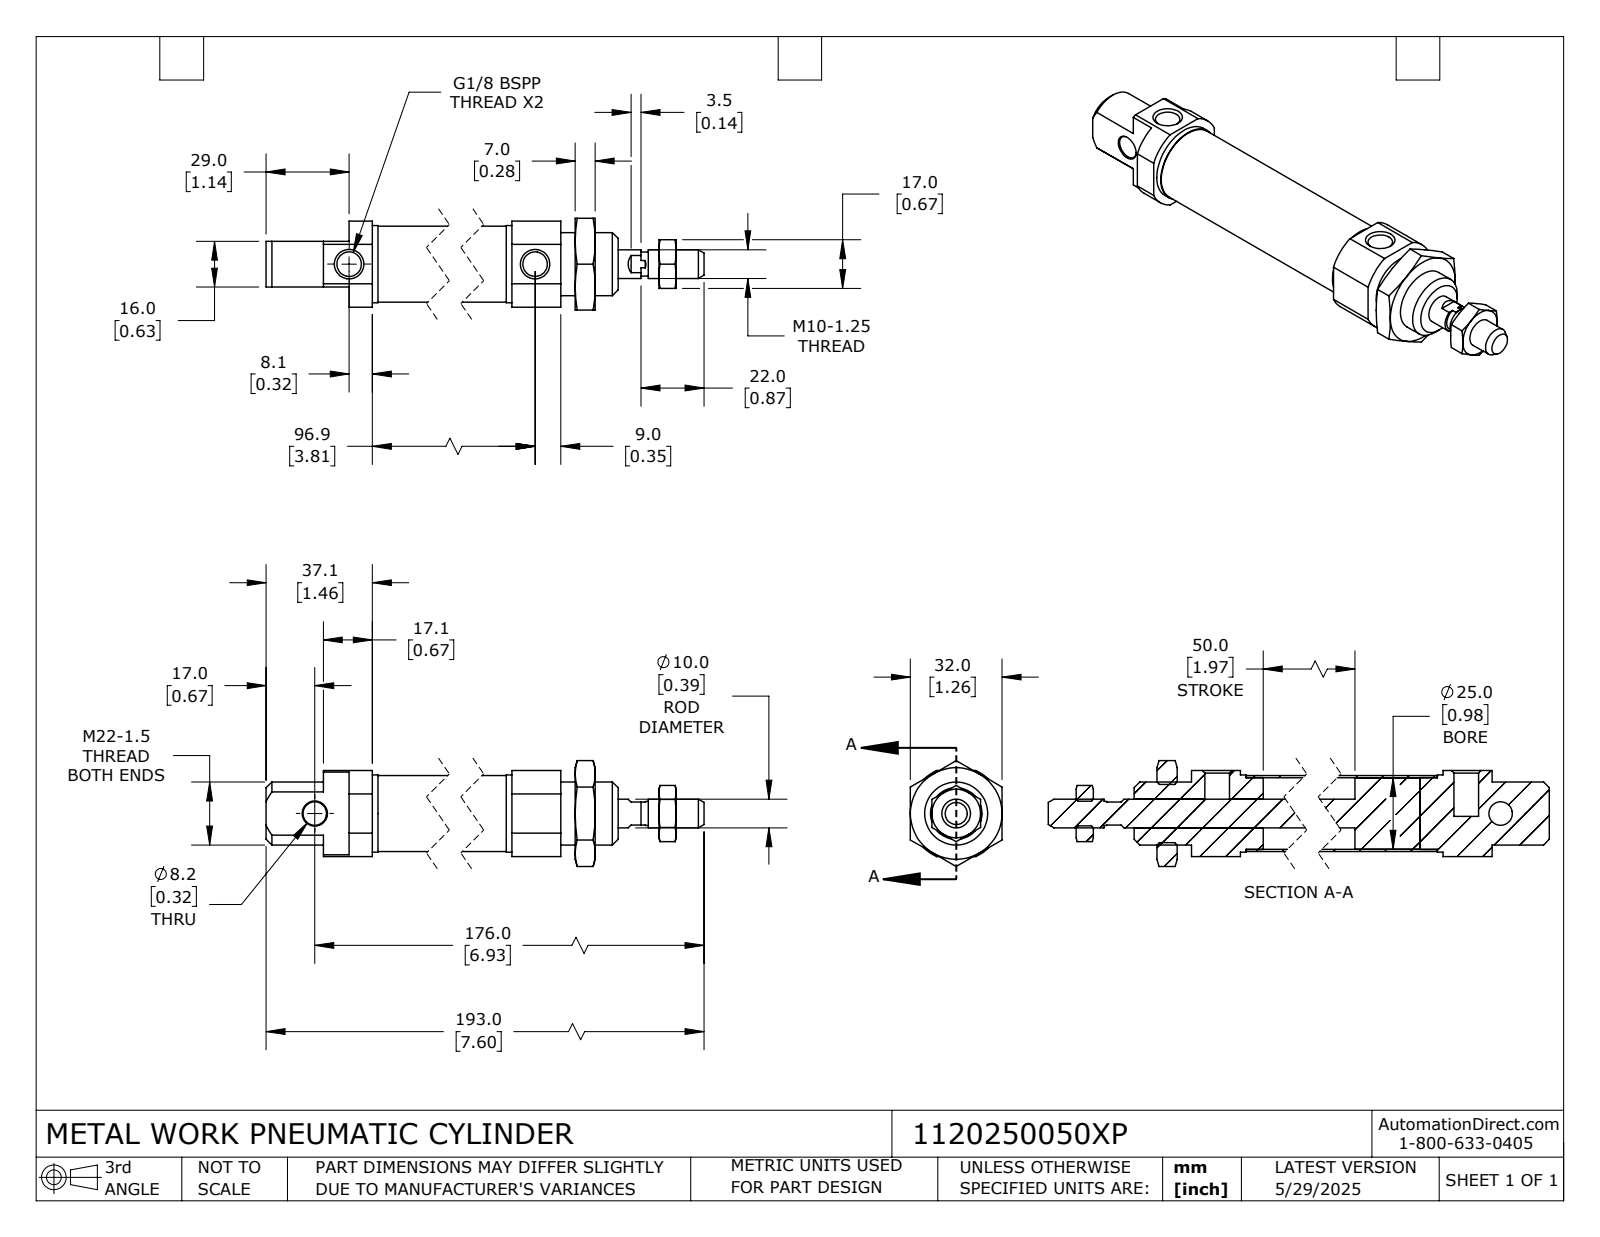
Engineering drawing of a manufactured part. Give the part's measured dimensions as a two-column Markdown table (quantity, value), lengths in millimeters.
| quantity | value |
| --- | --- |
| part name | 1120250050XP_BODY; 1120250050XP_ROD; 1120250050XP |
| STEP written by | SolidWorks 2024 (CONFIG_CONTROL_DESIGN) |
| units | millimeters |
| bodies | 6 solids, 144 faces (54 planar, 44 cylindrical, 46 other) |
| overall size | 193 × 36.95 × 32 |
| volume | 71 619 mm³ |
| surface area | 36 221 mm² |
| round holes (diameter × count) | 8.57 × 2, 8.2 × 1, 8.65 × 1, 20.38 × 1, 25 × 1 |
| round bosses / shafts (diameter × count) | 27 × 1, 26.52 × 1, 25.15 × 1, 22 × 1, 10 × 1, 8.4 × 1 |
| partial cylindrical surfaces (radius × count) | 16.5 × 1 |
| main face-to-face distances | 7, 8, 37.1, 23, 30, 117.9, 97.9, 25.1, 16, 50 |
| hole center spacings | 105 |
